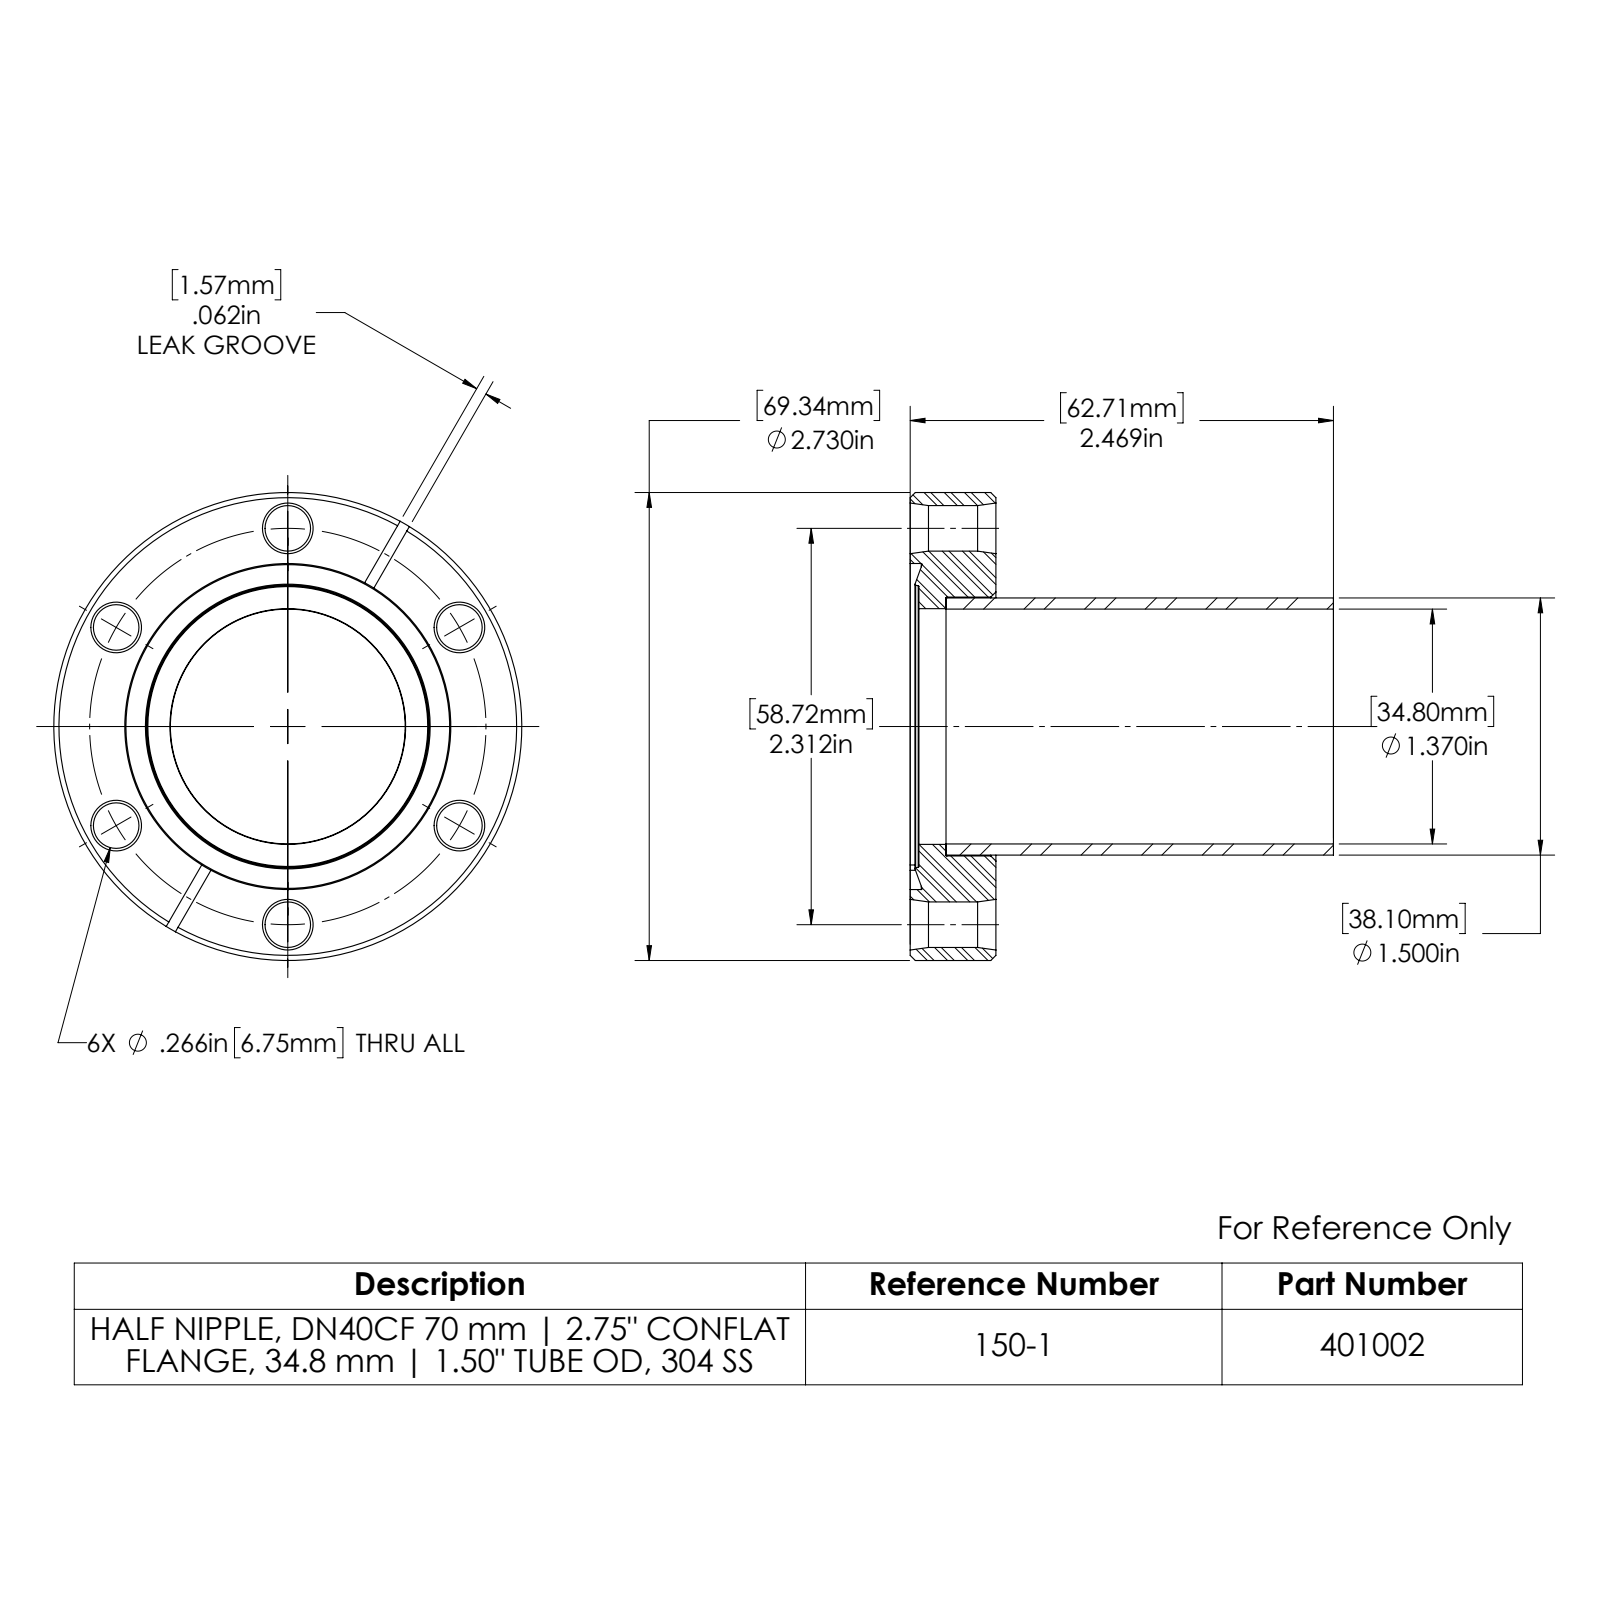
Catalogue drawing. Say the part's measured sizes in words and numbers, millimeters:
The part is named "110014-REV.A; 940102; 401002". Its 3-D file was written by "SolidWorks 2022 (AUTOMOTIVE_DESIGN)". It is 2 solids with 80 faces: 13 planar, 24 cylindrical and 43 other. Overall it measures 69.3 by 69.3 by 62.7 millimeters. Its volume is 41 020 cubic millimeters and its surface area 24 520 square millimeters. Round holes: 6 of diameter 6.8, 1 of diameter 34.8, 1 of diameter 34.9, 1 of diameter 38.4, 1 of diameter 48.3. Round bosses or shafts: 1 of diameter 69.3, 1 of diameter 38.1. The main face-to-face distances are 12.7, 11.4, 1.3, 7.4, 4, 5.3, 50, 57.4, 61.4, 62.7. The hole center spacings are 29.4, 50.9, 29.4, 58.7.
